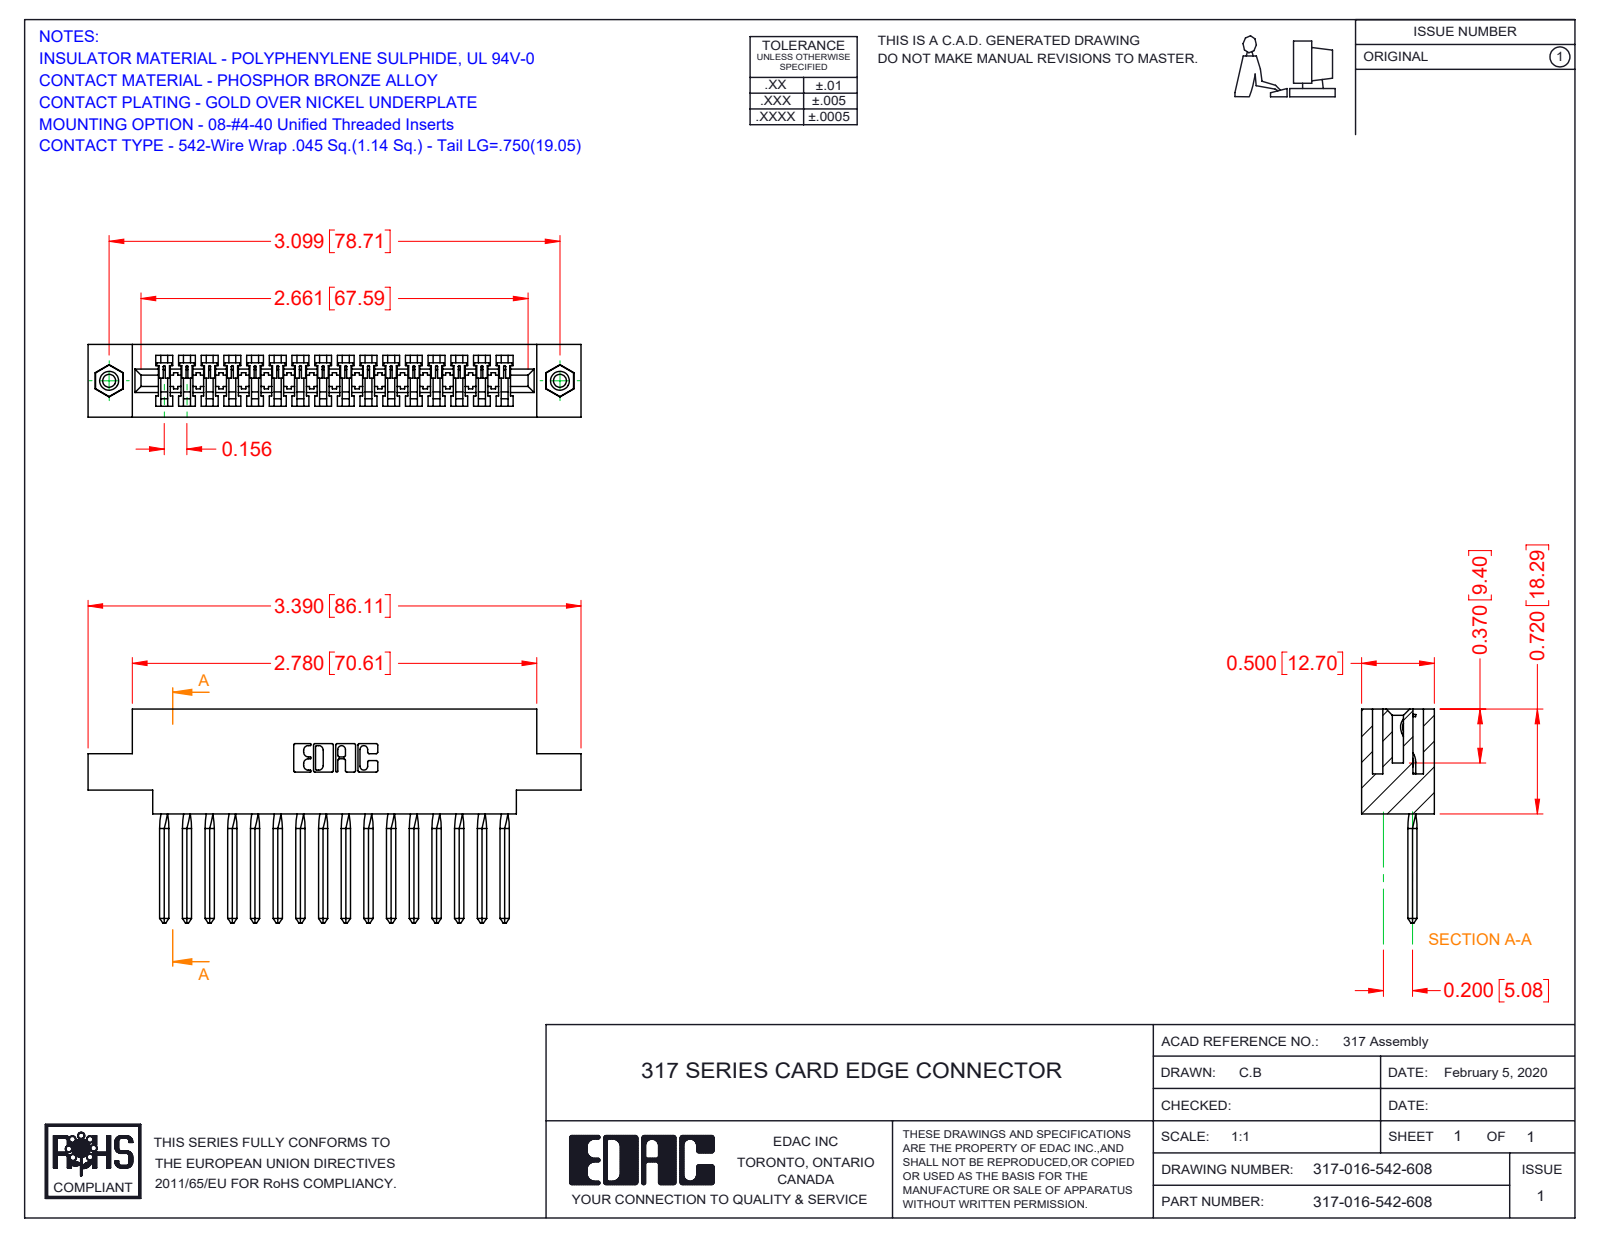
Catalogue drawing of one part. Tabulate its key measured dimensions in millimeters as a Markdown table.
| quantity | value |
| --- | --- |
| part name | 317-290-003_542; 317 Part_.156 Dia - TI; 317-016-542-608; 345-250-001_345-250-003-102 |
| STEP written by | SolidWorks 2016 (CONFIG_CONTROL_DESIGN) |
| units | millimeters |
| bodies | 19 solids, 1362 faces (1114 planar, 168 cylindrical, 80 other) |
| overall size | 86.1 × 37.3 × 12.7 |
| volume | 12 600 mm³ |
| surface area | 14 810 mm² |
| round holes (diameter × count) | 2.3 × 2, 3.2 × 2, 4 × 2 |
| round bosses / shafts (diameter × count) | 3.9 × 2 |
| partial cylindrical surfaces (radius × count) | 0.2 × 32, 0.3 × 22, 0.2 × 6, 0.8 × 6, 0.7 × 3, 1.9 × 1, 2.3 × 1, 2.5 × 1 |
| main face-to-face distances | 12.7, 1.9, 10.8, 2.8, 8.9, 1.7, 3.5, 5.6, 18.3, 5.4 |
| hole center spacings | 78.7 |
